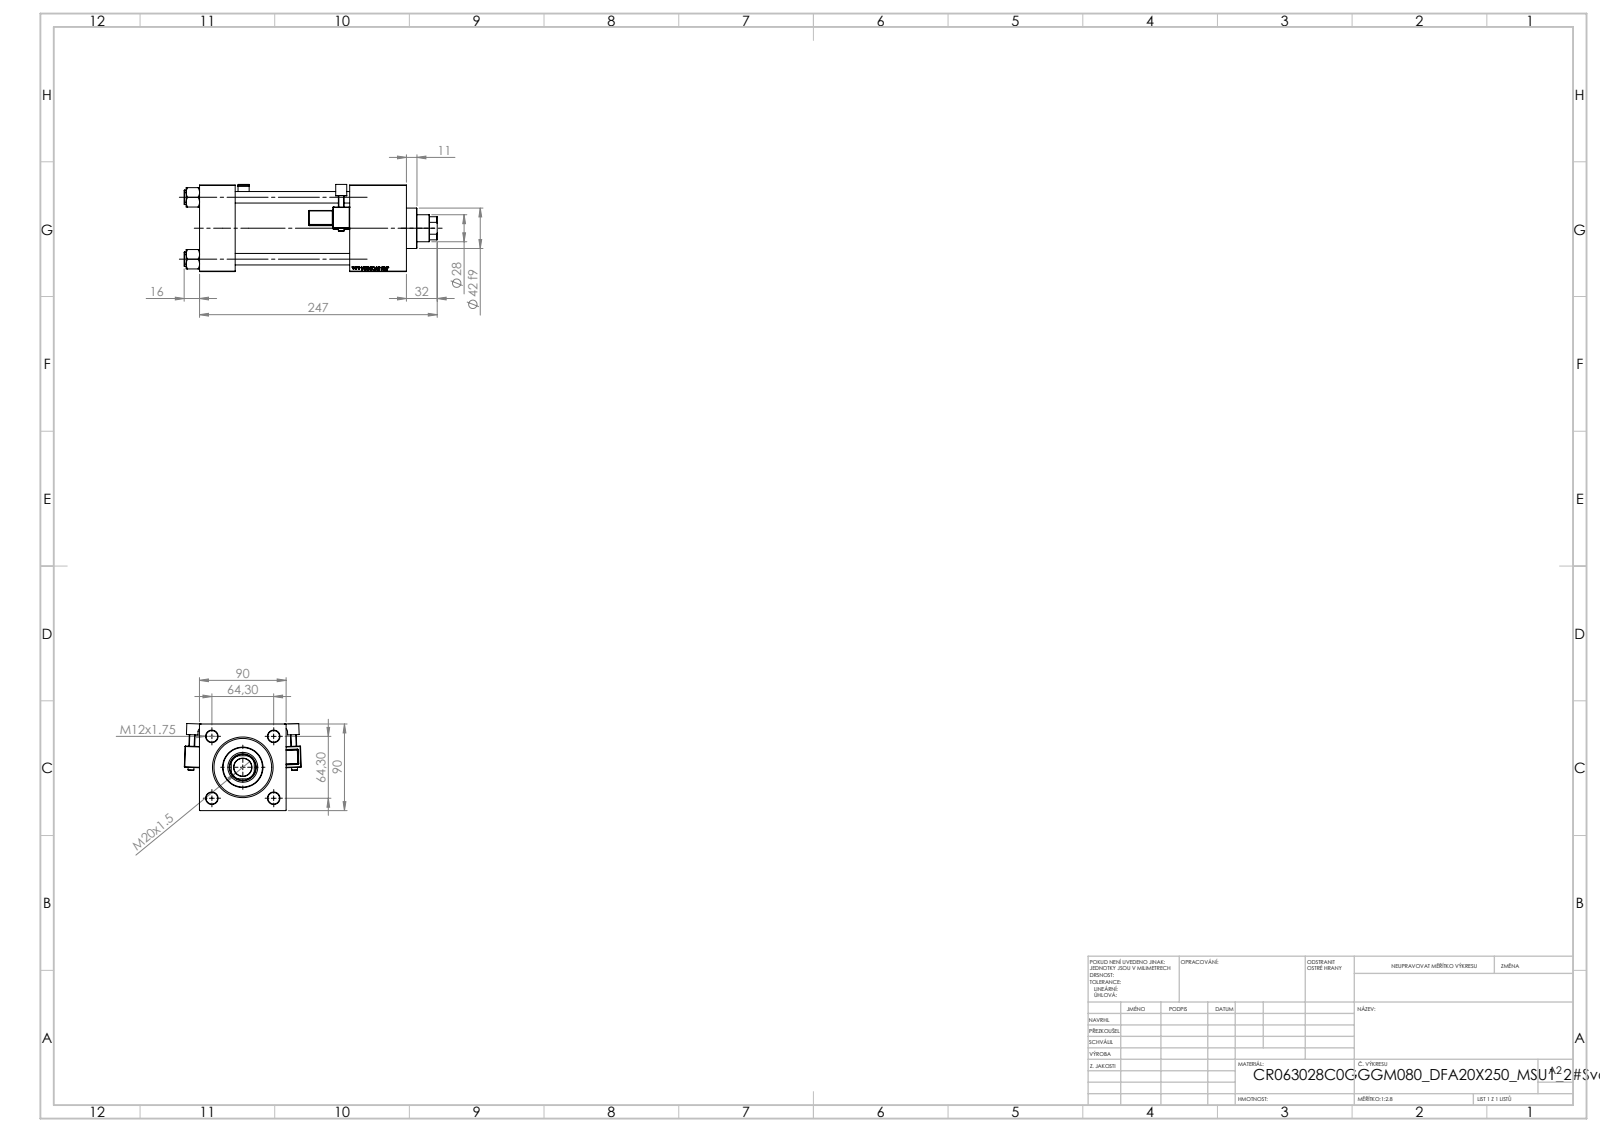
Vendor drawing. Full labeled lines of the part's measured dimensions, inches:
Part name (STEP PRODUCT): V215CR_C_TYCINKA; FEMALE_PART_FOR_DFA; V215CR_VCP_C; V215_VC_A (+3 more)
STEP written by: SolidWorks 2019 (CONFIG_CONTROL_DESIGN)
Units: inches
Bodies: 14 solids, 1336 faces (596 planar, 156 cylindrical, 584 other)
Overall size (bounding box): 10.354 × 4.786 × 3.564
Volume: 67.98 in³ · Surface area: 369.3 in²
Round holes (diameter × count): ⌀0.472 ×4, ⌀0.276 ×2, ⌀0.825 ×2, ⌀1.181 ×2, ⌀0.728 ×1, ⌀1.102 ×1, ⌀1.22 ×1, ⌀1.969 ×1, ⌀2.362 ×1, ⌀2.48 ×1
Round bosses / shafts (diameter × count): ⌀0.591 ×4, ⌀0.236 ×2, ⌀2.717 ×1, ⌀1.654 ×1, ⌀1.417 ×1, ⌀1.181 ×1, ⌀0.787 ×1, ⌀0.709 ×1
Partial cylindrical surfaces — rounded edges, fillets, slot ends (radius × count): R0.02 ×48, R0.039 ×2, R0.098 ×2, R0.157 ×2, R0.295 ×1, R0.472 ×1, R0.531 ×1
Main face-to-face distances: 3.543, 1.457, 8.465, 7.008, 6.142, 4.685, 2.323, 7.335, 5.878, 1.193
Hole centre spacings: 1.79, 2.531, 3.58, 6.201
